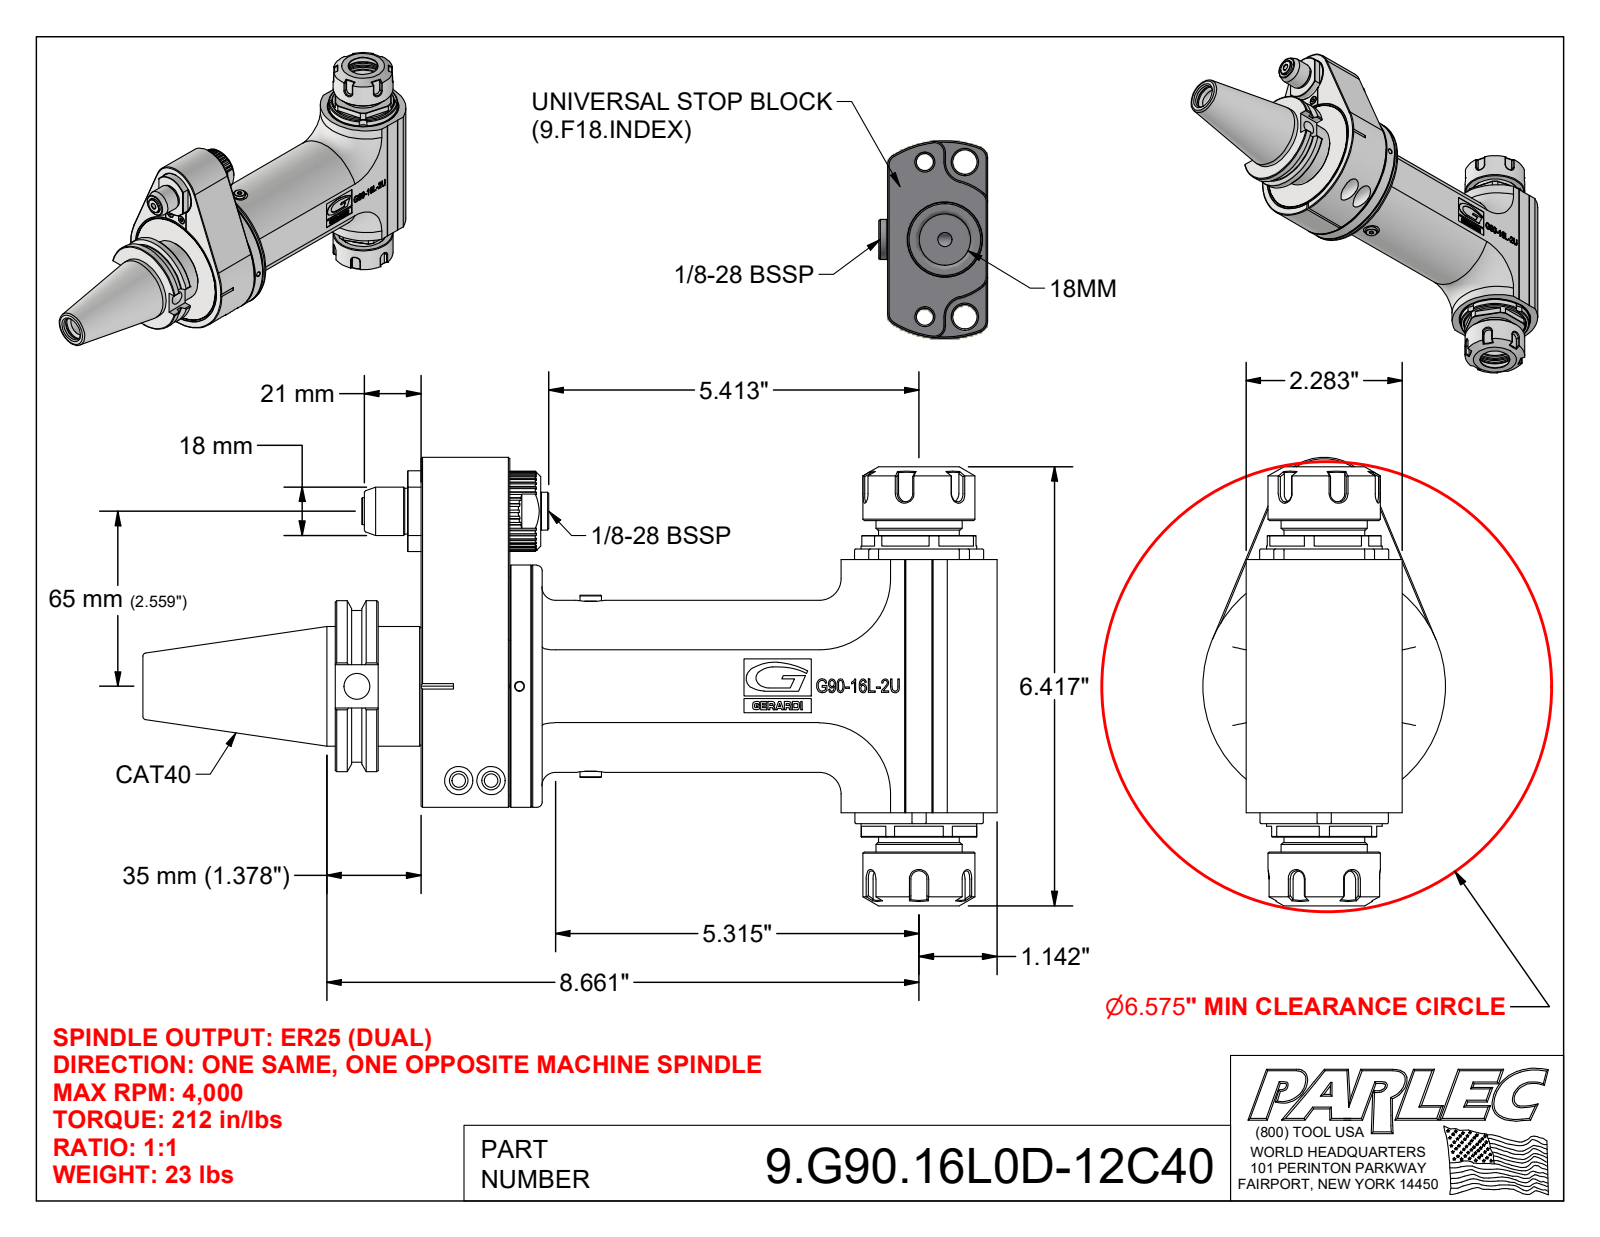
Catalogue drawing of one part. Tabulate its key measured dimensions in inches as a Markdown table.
| quantity | value |
| --- | --- |
| part name | 9.G90.16L0D-12C40; 9_G90_16LD; 9_GA1_446_1 (Classic, Type 1, Cat40, 65mm) |
| STEP written by | Autodesk Inventor 2022 (AUTOMOTIVE_DESIGN) |
| units | inches |
| bodies | 45 solids, 1506 faces (687 planar, 303 cylindrical, 516 other) |
| overall size | 12.496 × 6.555 × 3.543 |
| volume | 62.76 in³ |
| surface area | 309.5 in² |
| round holes (diameter × count) | 0.165 × 8, 0.197 × 5, 0.236 × 4, 0.157 × 2, 0.276 × 2, 0.335 × 2, 0.413 × 2, 0.433 × 2, 0.551 × 2, 0.709 × 2, 1.201 × 2, 1.654 × 2 |
| round bosses / shafts (diameter × count) | 0.157 × 3, 1.181 × 2, 0.315 × 2, 3.543 × 1, 3.071 × 1, 2.5 × 1, 2.219 × 1, 1.89 × 1 |
| partial cylindrical surfaces (radius × count) | 0.118 × 18, 0.059 × 16, 0.049 × 8, 0.098 × 3, 1.26 × 3, 0.085 × 2, 0.197 × 2, 0.079 × 1 |
| main face-to-face distances | 1.299, 0.197, 0.354, 2.283, 0.118, 0.984, 1.181, 0.315, 0.976, 0.205 |
| hole center spacings | 1.476, 2.557, 0.764, 1.476, 2.088, 2.953, 0.366, 0.817 |
